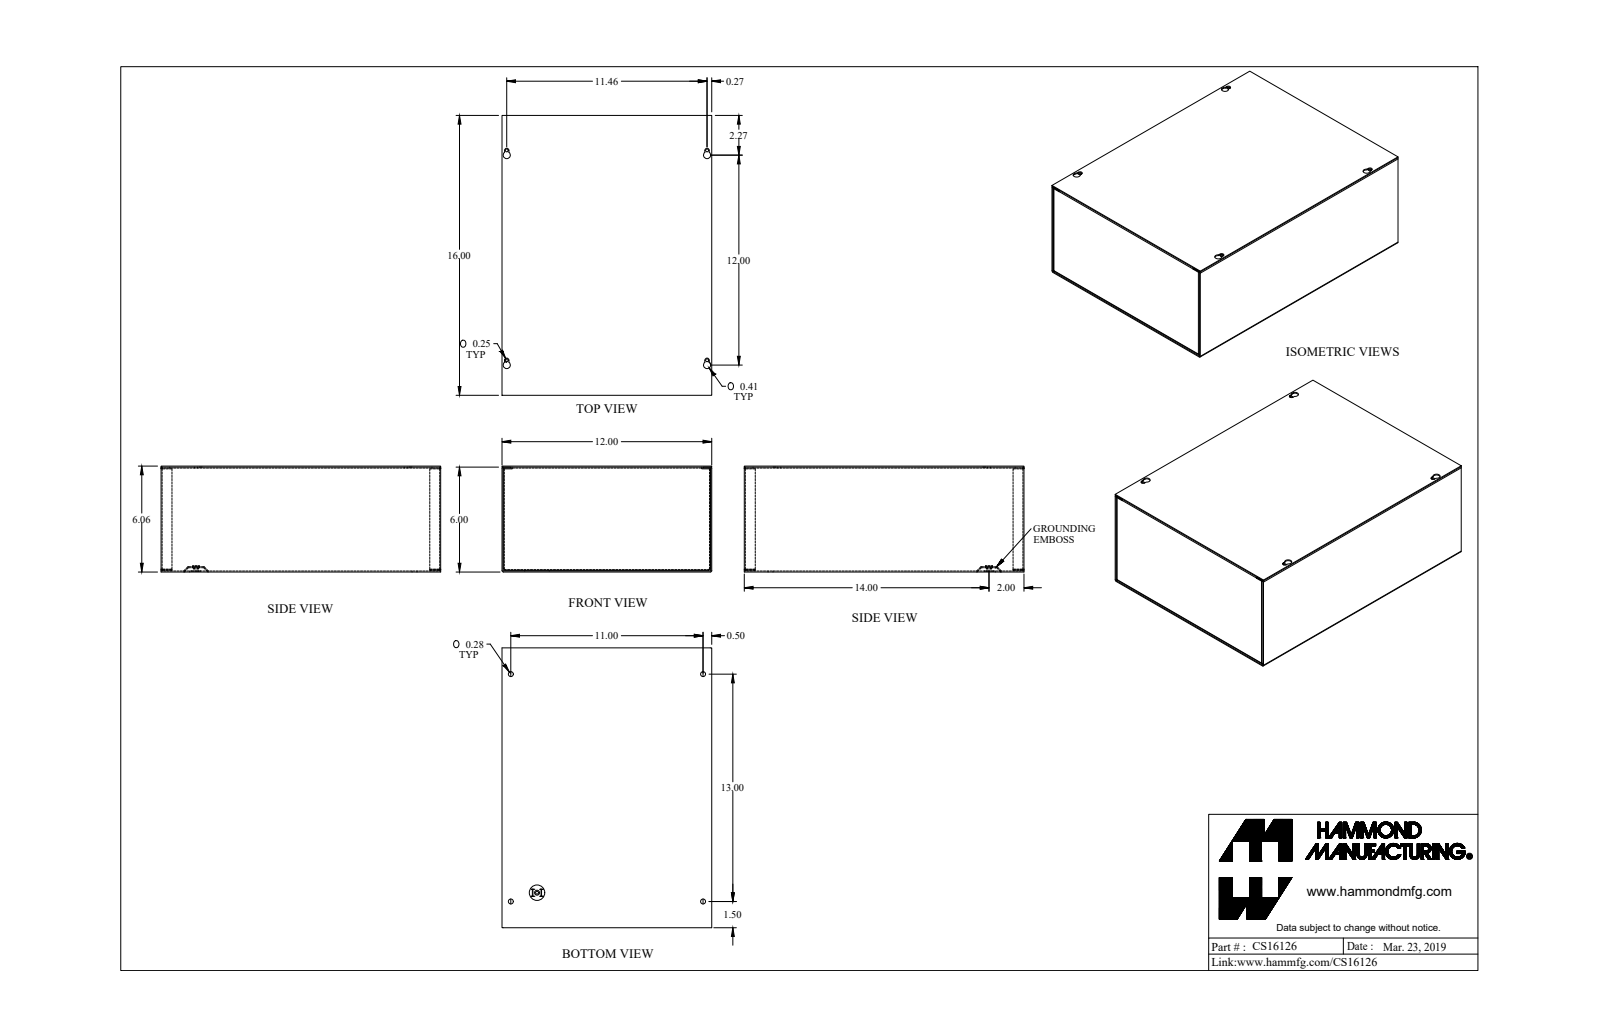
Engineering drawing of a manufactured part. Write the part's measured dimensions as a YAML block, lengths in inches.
part_name: "CS16126_Default"
step_written_by: "SolidWorks 2019 (CONFIG_CONTROL_DESIGN)"
units: inches
bodies: {solids: 4, faces: 205, planar: 125, cylindrical: 72, other: 8}
overall_size: [16, 12, 6.057]
volume: 43.36
surface_area: 1534
round_holes:
  - {diameter: 0.17, count: 5}
  - {diameter: 0.281, count: 4}
  - {diameter: 0.5, count: 1}
round_bosses_or_shafts:
  - {diameter: 0.492, count: 1}
  - {diameter: 0.284, count: 1}
partial_cylinders:
  - {radius: 0.029, count: 12}
  - {radius: 0.086, count: 12}
  - {radius: 0.057, count: 8}
  - {radius: 0.125, count: 4}
  - {radius: 0.203, count: 4}
face_to_face_distances: [0.057, 6, 5.943, 6.057, 11.943, 15.943, 12, 11.886, 16, 15.886]
hole_center_spacings: [0.55, 11.241, 12.502, 16.804, 11, 11.46, 12, 13]
